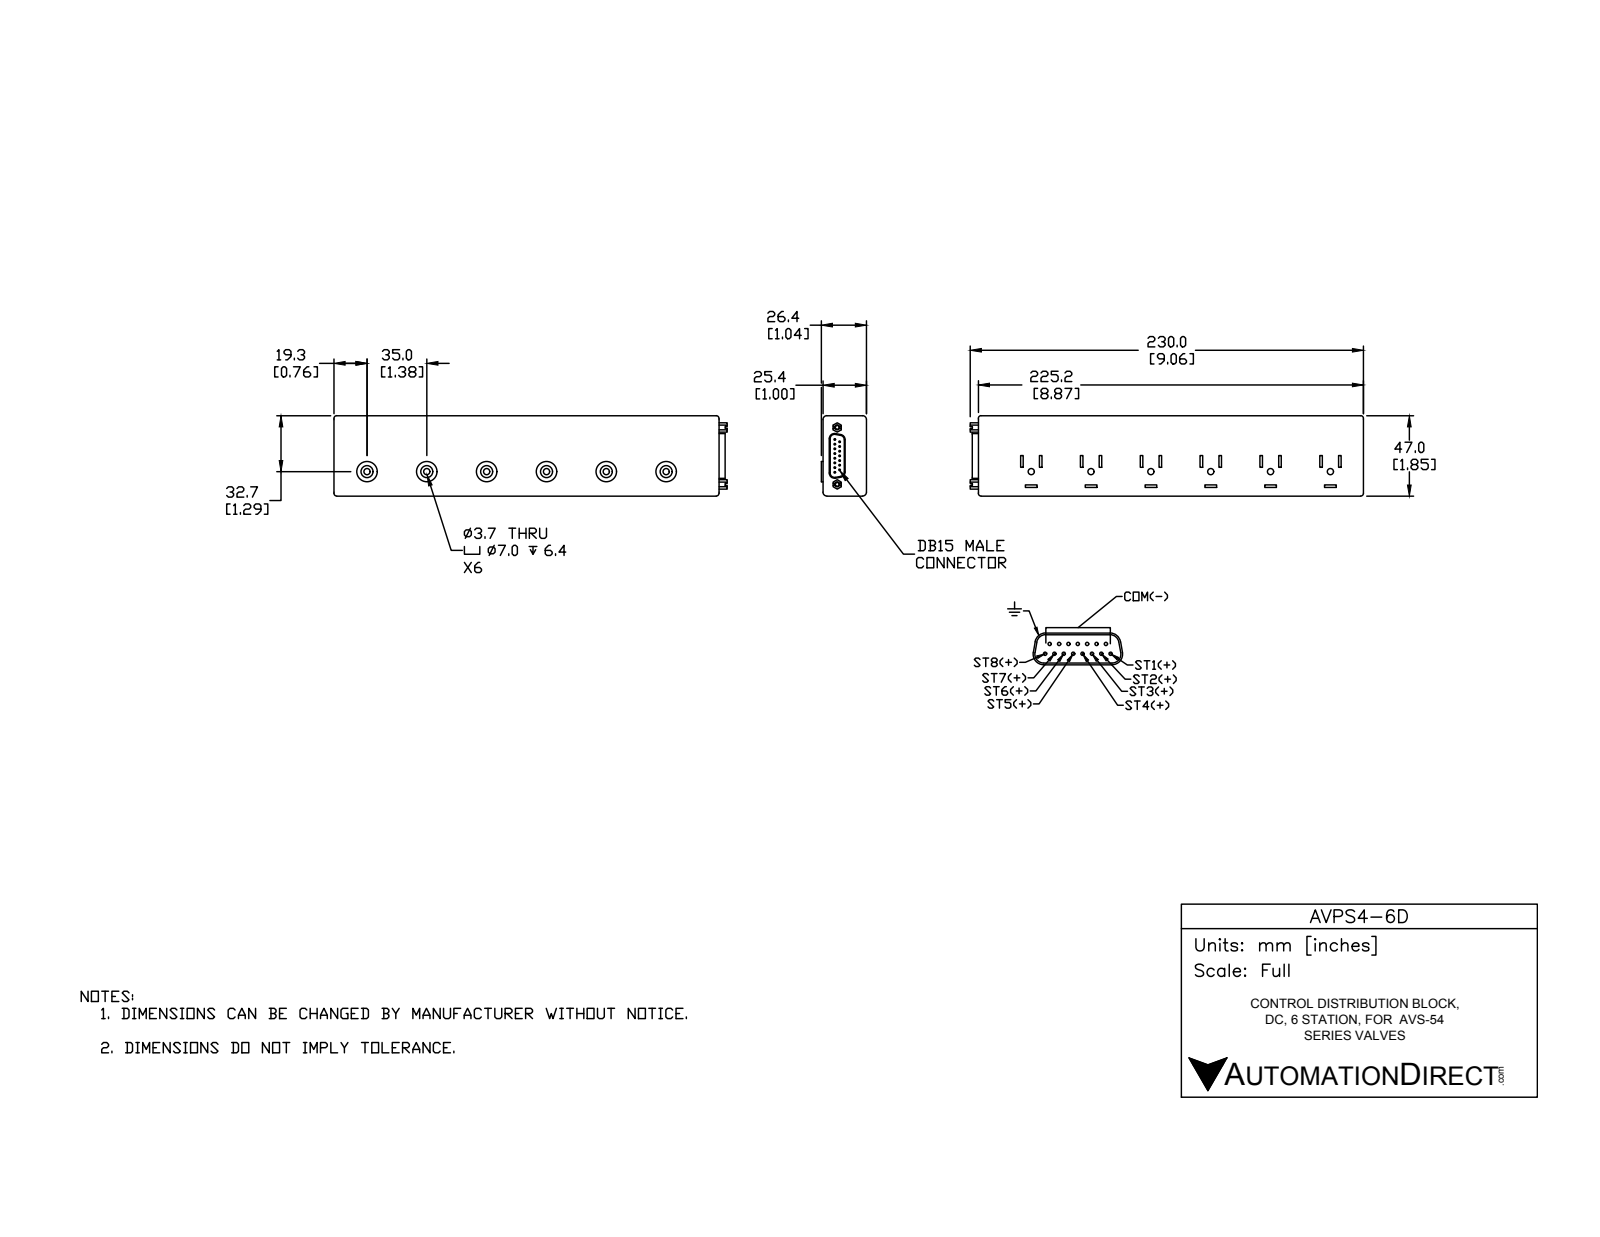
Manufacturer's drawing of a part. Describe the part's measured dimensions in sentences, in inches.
The part is named "AVPS4-6D". Its 3-D file was written by "SolidWorks 2016 (AUTOMOTIVE_DESIGN)". It is 1 solid with 265 faces: 161 planar, 92 cylindrical and 12 other. Overall it measures 9.057 by 1.85 by 1.04 inches. Its volume is 16.12 cubic inches and its surface area 60.89 square inches. Round holes: 6 of diameter 0.145, 6 of diameter 0.275, 2 of diameter 0.089. Round bosses or shafts: 15 of diameter 0.039, 6 of diameter 0.469. Partial cylindrical surfaces (rounded edges, fillets, slot ends): 8 of radius 0.062, 4 of radius 0.09, 4 of radius 0.102, 4 of radius 0.122. The main face-to-face distances are 1, 1.85, 8.868, 0.059, 0.04, 1.04, 1.378, 0.25, 0.79, 0.433. The hole center spacings are 1.378, 4.134, 2.756, 2.756, 5.512, 1.311, 1.378, 6.89.
